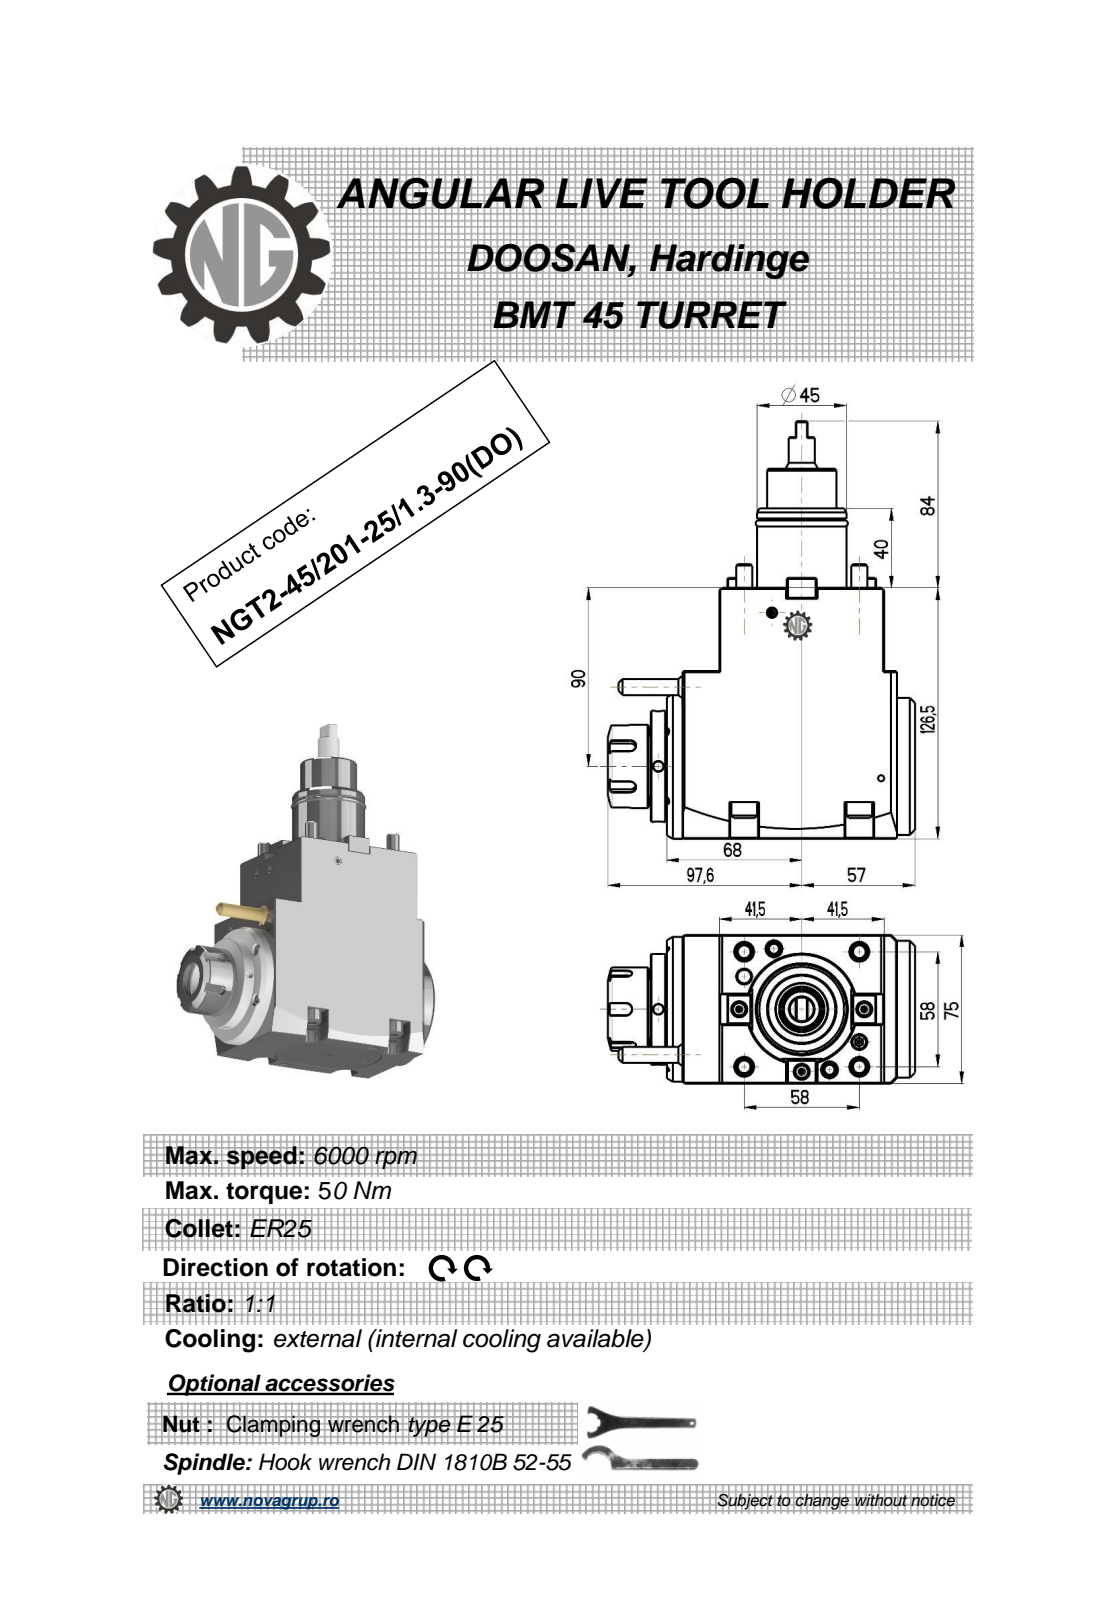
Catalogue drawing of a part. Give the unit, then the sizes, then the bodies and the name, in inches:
Units: inches
Overall size (bounding box): 8.287 × 6.087 × 2.953
Round holes (diameter × count): ⌀0.197 ×3, ⌀0.268 ×2, ⌀0.118 ×1, ⌀0.799 ×1
Round bosses / shafts (diameter × count): ⌀0.512 ×5, ⌀0.315 ×5, ⌀2.874 ×1, ⌀2.717 ×1, ⌀2.205 ×1, ⌀1.772 ×1, ⌀1.693 ×1, ⌀1.654 ×1
Partial cylindrical surfaces — rounded edges, fillets, slot ends (radius × count): R0.118 ×5, R0.276 ×4, R0.01 ×2, R0.031 ×2, R21.654 ×2, R0.098 ×1
Main face-to-face distances: 2.953, 0.315, 4.98, 0.61, 3.268, 3.878, 4.567, 0.354, 1.043, 4.311
Hole centre spacings: 1.817, 1.822, 2.627, 4.039
Volume: 69.2 in³ · Surface area: 135.6 in²
Bodies: 2 solids, 367 faces (183 planar, 79 cylindrical, 105 other)
Part name (STEP PRODUCT): NGT2_45_201_25_1_3_90_DO
STEP written by: PRO/ENGINEER BY PARAMETRIC TECHNOLOGY CORPORATION, 2010280 (CONFIG_CONTROL_DESIGN)
